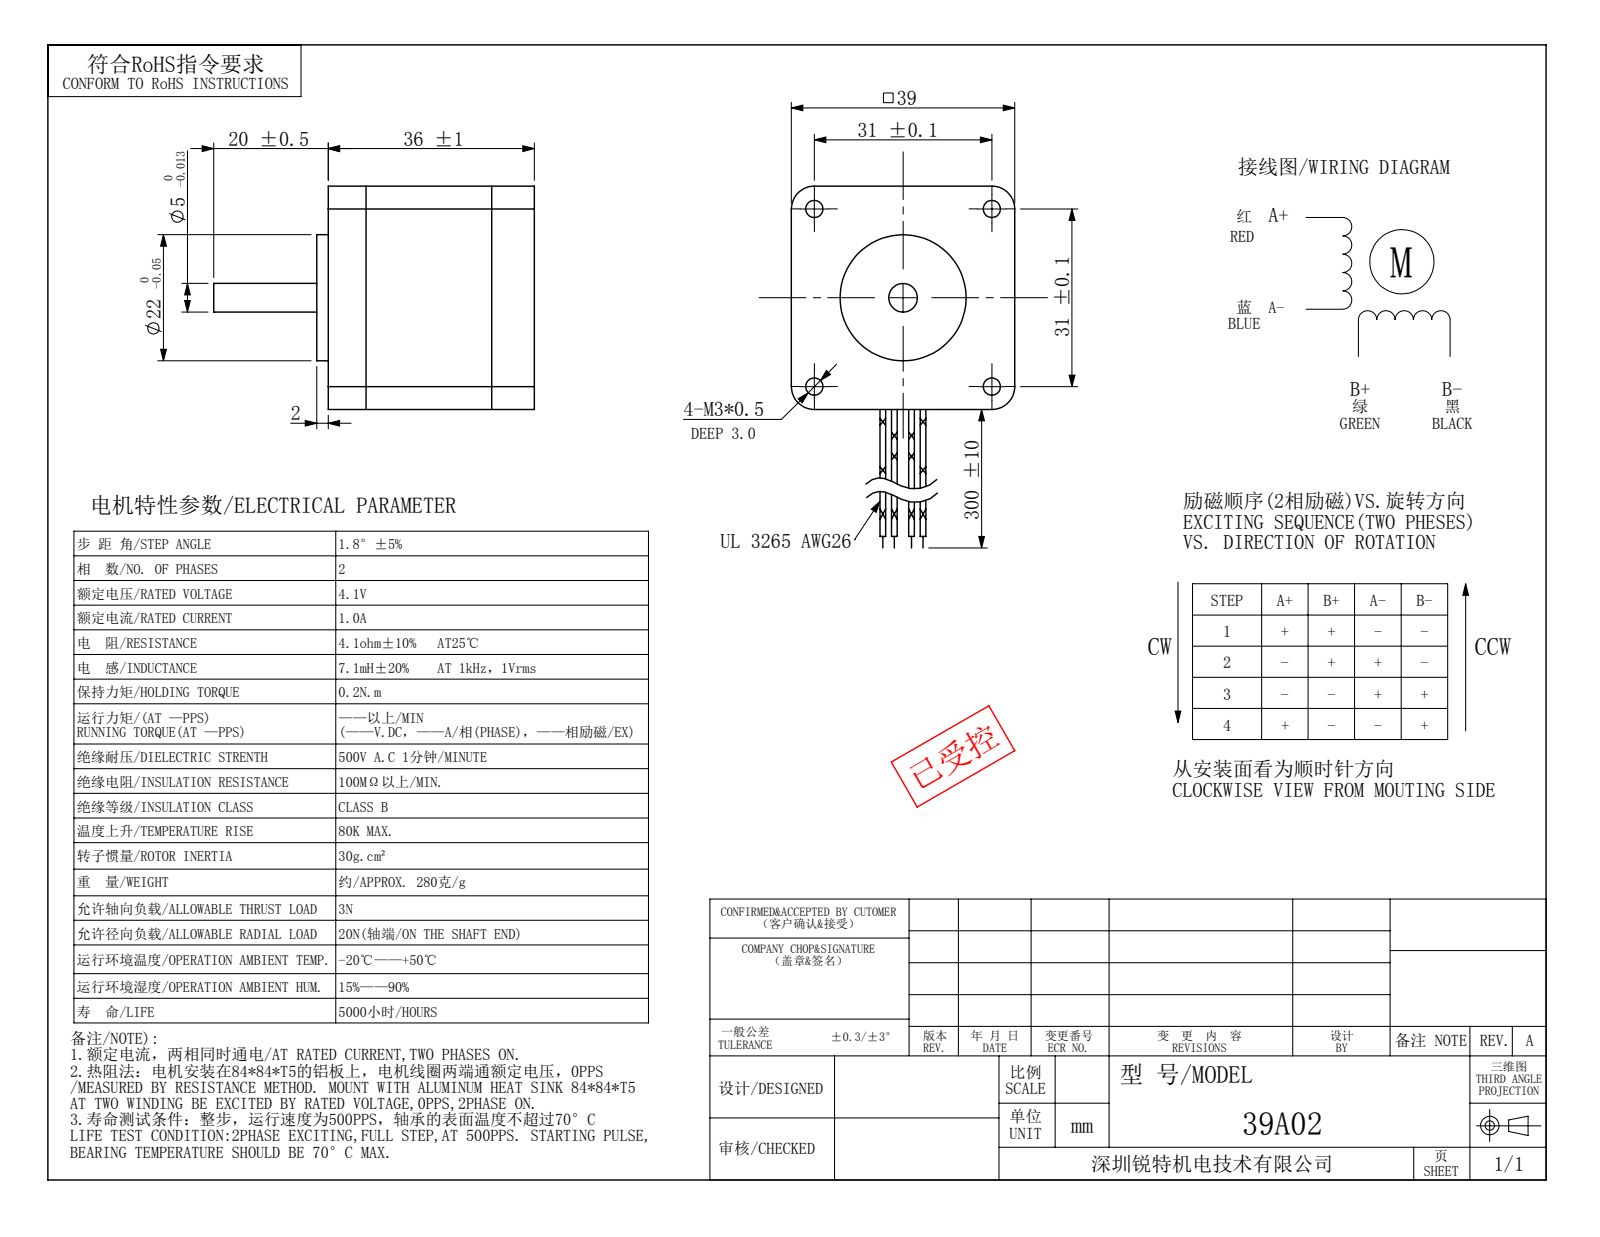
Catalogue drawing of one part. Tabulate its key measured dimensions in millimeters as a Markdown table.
| quantity | value |
| --- | --- |
| part name | 39HS36-L0520-001 |
| STEP written by | SolidWorks 2014 (AUTOMOTIVE_DESIGN) |
| units | millimeters |
| bodies | 1 solid, 28 faces (12 planar, 16 cylindrical, 0 other) |
| overall size | 56 × 39 × 39 |
| volume | 55 290 mm³ |
| surface area | 8 917 mm² |
| round holes (diameter × count) | 3 × 4 |
| round bosses / shafts (diameter × count) | 22 × 1, 5 × 1 |
| partial cylindrical surfaces (radius × count) | 4 × 4 |
| main face-to-face distances | 39, 36, 38, 2, 33, 3, 5, 56, 23, 20 |
| hole center spacings | 31, 43.84 |
